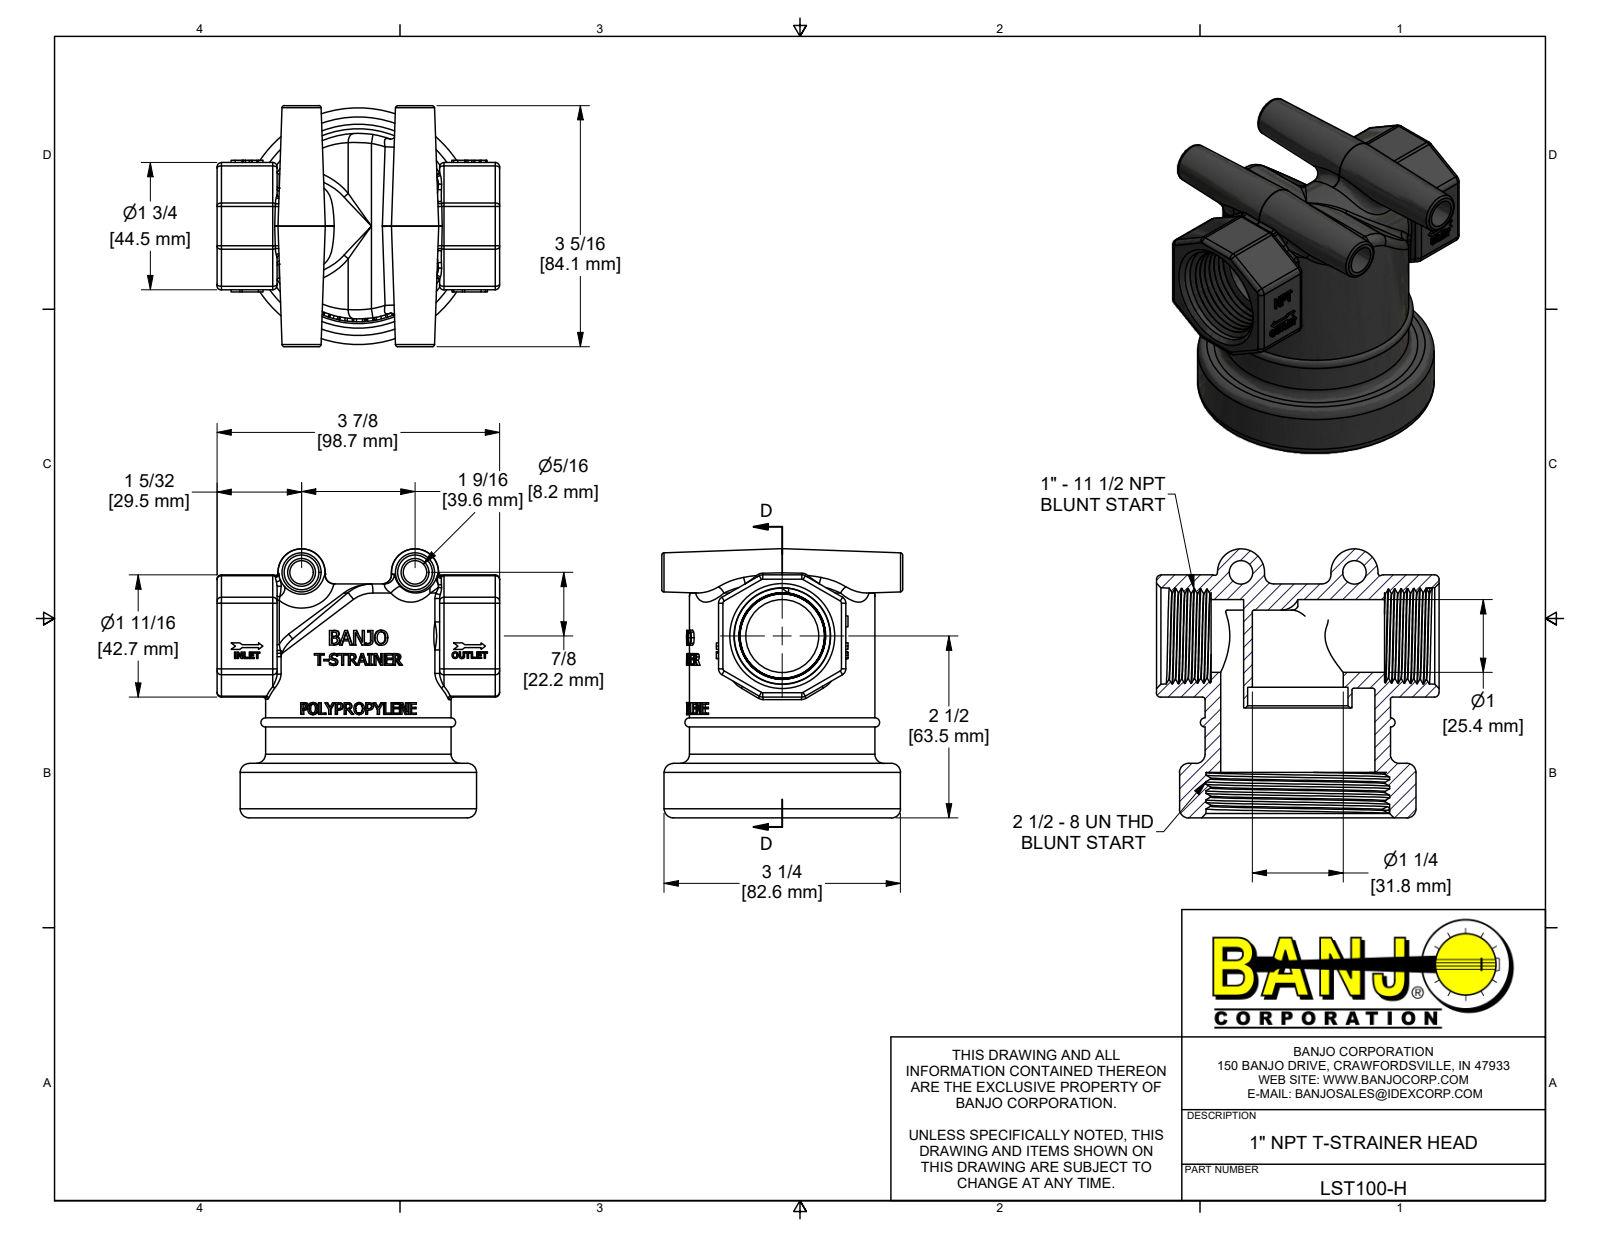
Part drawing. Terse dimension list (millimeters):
name: LST100H
written by: Mechanical Desktop 2009 (CONFIG_CONTROL_DESIGN)
unit: mm
bodies: 1 solid, 330 faces (43 planar, 76 cylindrical, 211 other)
size: 98.3 × 93.6 × 84.2
volume: 193 000 mm³; area: 68 650 mm²
holes: 1× ⌀19.1, 1× ⌀31.8, 1× ⌀35.1, 1× ⌀53.8
bosses: 1× ⌀82.6, 1× ⌀65
rounds: 43× R0.8, 1× R3.2, 1× R18.7, 1× R18.9, 1× R19.1
face distances: 44.5, 72.5, 19.1, 53.5, 44.5, 98.3, 17.7, 80.6, 81.7, 62.6
